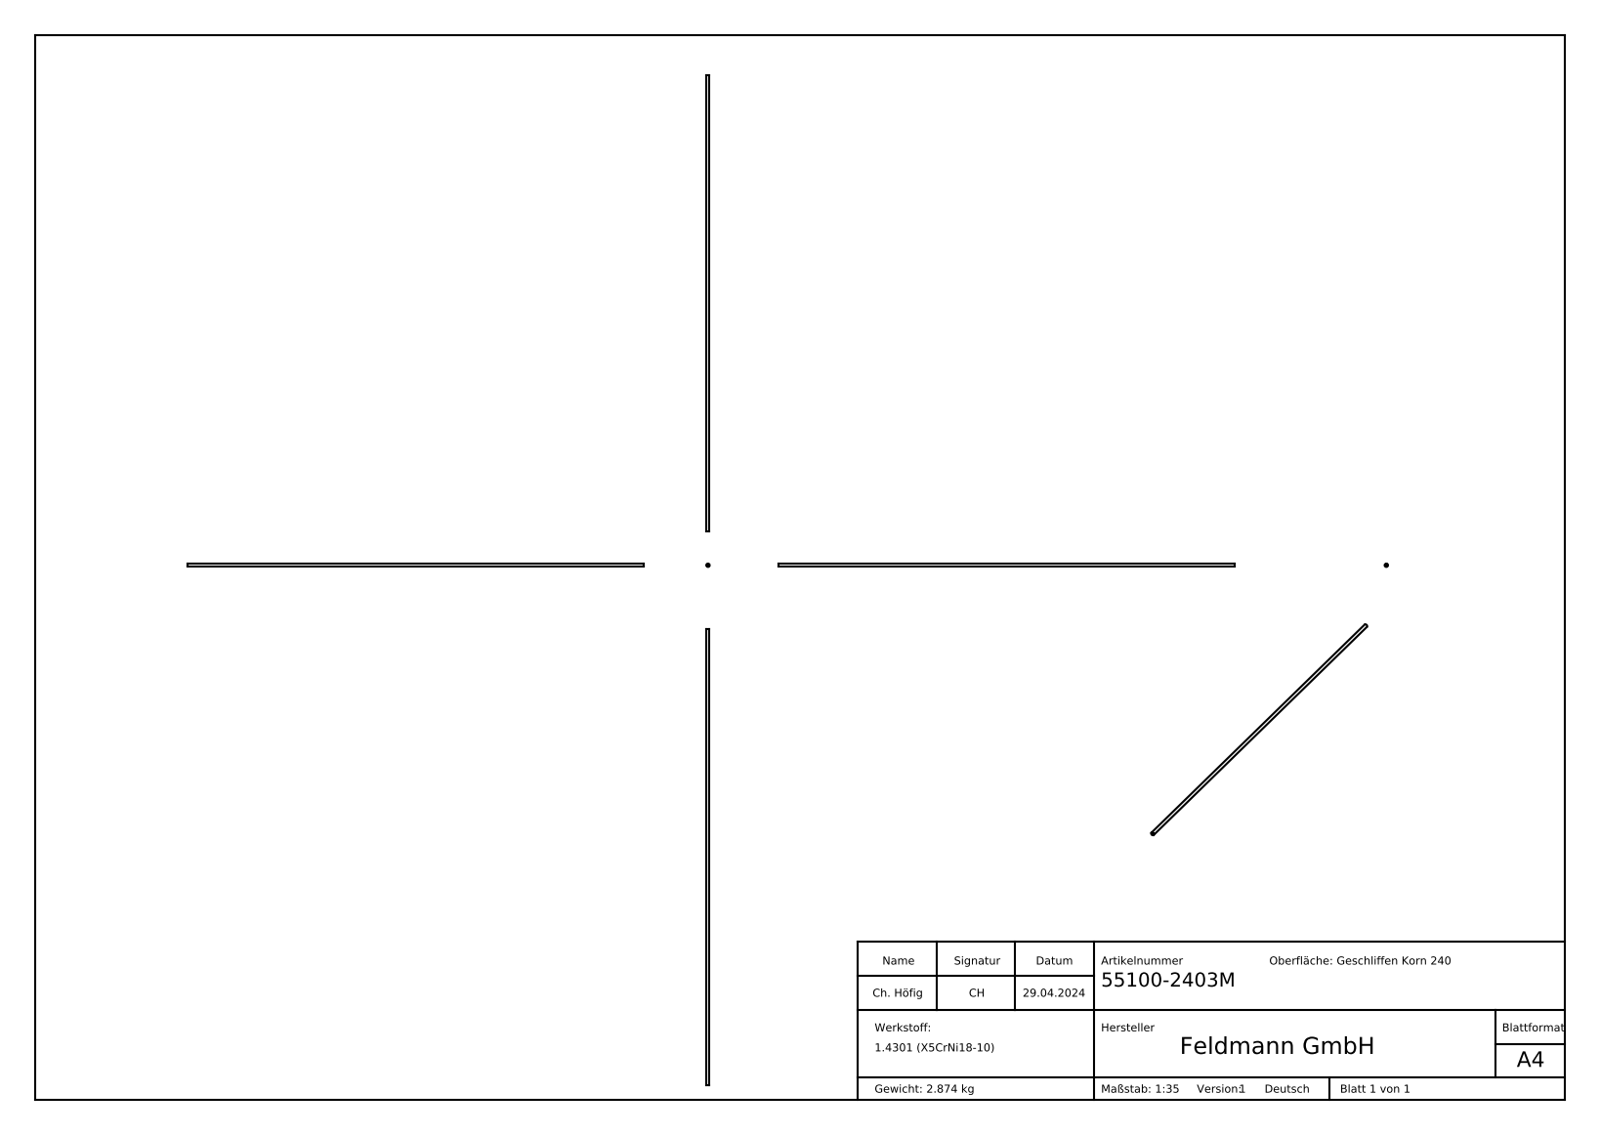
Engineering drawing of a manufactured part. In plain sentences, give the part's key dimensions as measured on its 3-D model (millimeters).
The part is named "55100-2403M". Its 3-D file was written by "SolidWorks 2018 (CONFIG_CONTROL_DESIGN)". It is 1 solid with 295 faces: 135 planar, 29 cylindrical and 131 other. Overall it measures 3000 by 21.3 by 21.3 millimeters. Its volume is 363 796 cubic millimeters and its surface area 364 047 square millimeters. Round holes: 1 of diameter 17.3. Round bosses or shafts: 1 of diameter 21.3. Partial cylindrical surfaces (rounded edges, fillets, slot ends): 1 of radius 8.75. The main face-to-face distances are 3000, 1.57, 1.78, 2.41, 0.73, 2.61, 0.65, 0.79, 2.24, 2.45.
